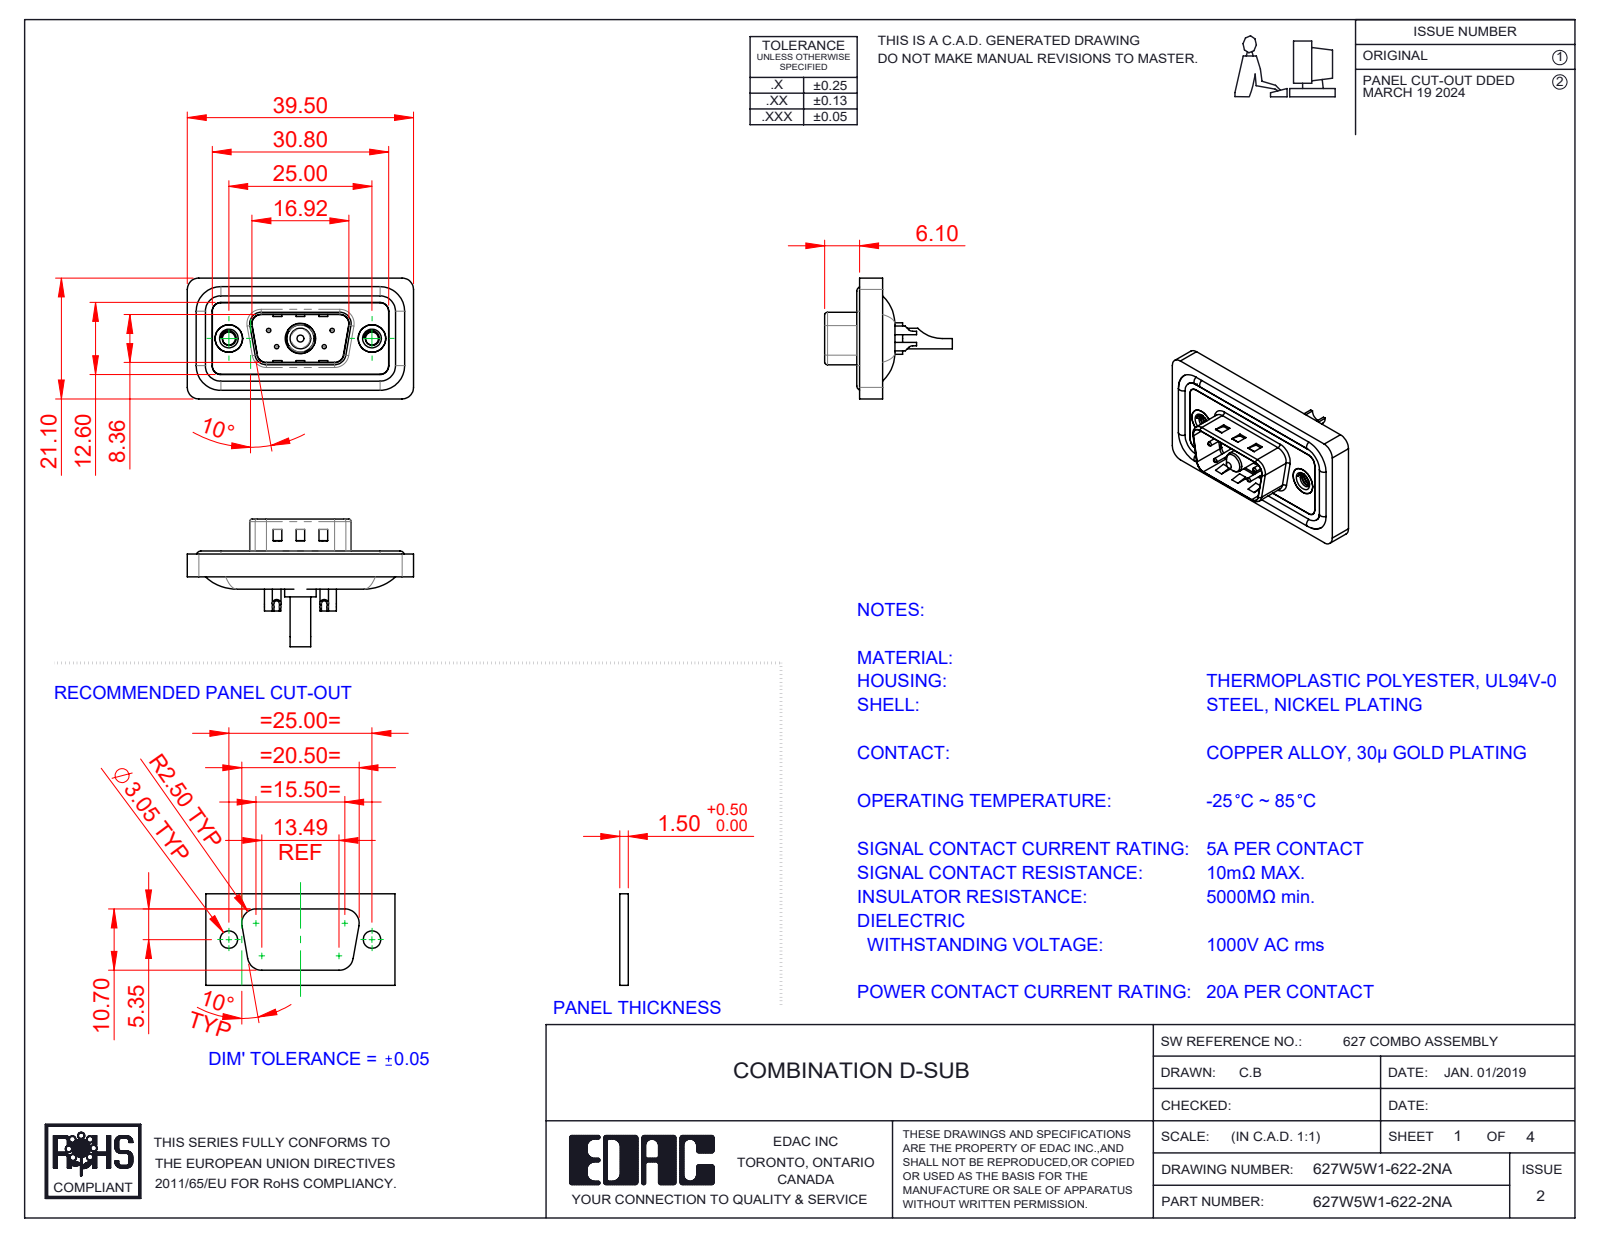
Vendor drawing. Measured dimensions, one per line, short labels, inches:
name: Power Pin_20A SC; 627Combo Contact Row 1_22; 627Combo Waterproof Housing_09 Contacts; 627Combo Housing_5W1 (+5 more)
written by: SolidWorks 2023 (CONFIG_CONTROL_DESIGN)
unit: in
bodies: 13 solids, 603 faces (194 planar, 268 cylindrical, 141 other)
size: 1.555 × 0.878 × 0.831
volume: 0.269 in³; area: 10.93 in²
holes: 4× ⌀0.03, 4× ⌀0.039, 4× ⌀0.063, 4× ⌀0.079, 2× ⌀0.089, 2× ⌀0.157, 2× ⌀0.189, 2× ⌀0.197, 1× ⌀0.106, 1× ⌀0.191, 1× ⌀0.209
bosses: 4× ⌀0.063, 4× ⌀0.059, 2× ⌀0.193, 1× ⌀0.217, 1× ⌀0.205, 1× ⌀0.187, 1× ⌀0.148, 1× ⌀0.142
rounds: 22× R0.059, 18× R0.079, 8× R0.02, 8× R0.063, 6× R0.039, 4× R0.01, 4× R0.024, 4× R0.026
face distances: 0.016, 0.043, 0.114, 0.063, 0.122, 0.02, 0.059, 0.098, 0.157, 0.031
hole spacings: 0.124, 0.225, 0.28, 0.492, 0.713, 0.173, 0.173, 0.327
